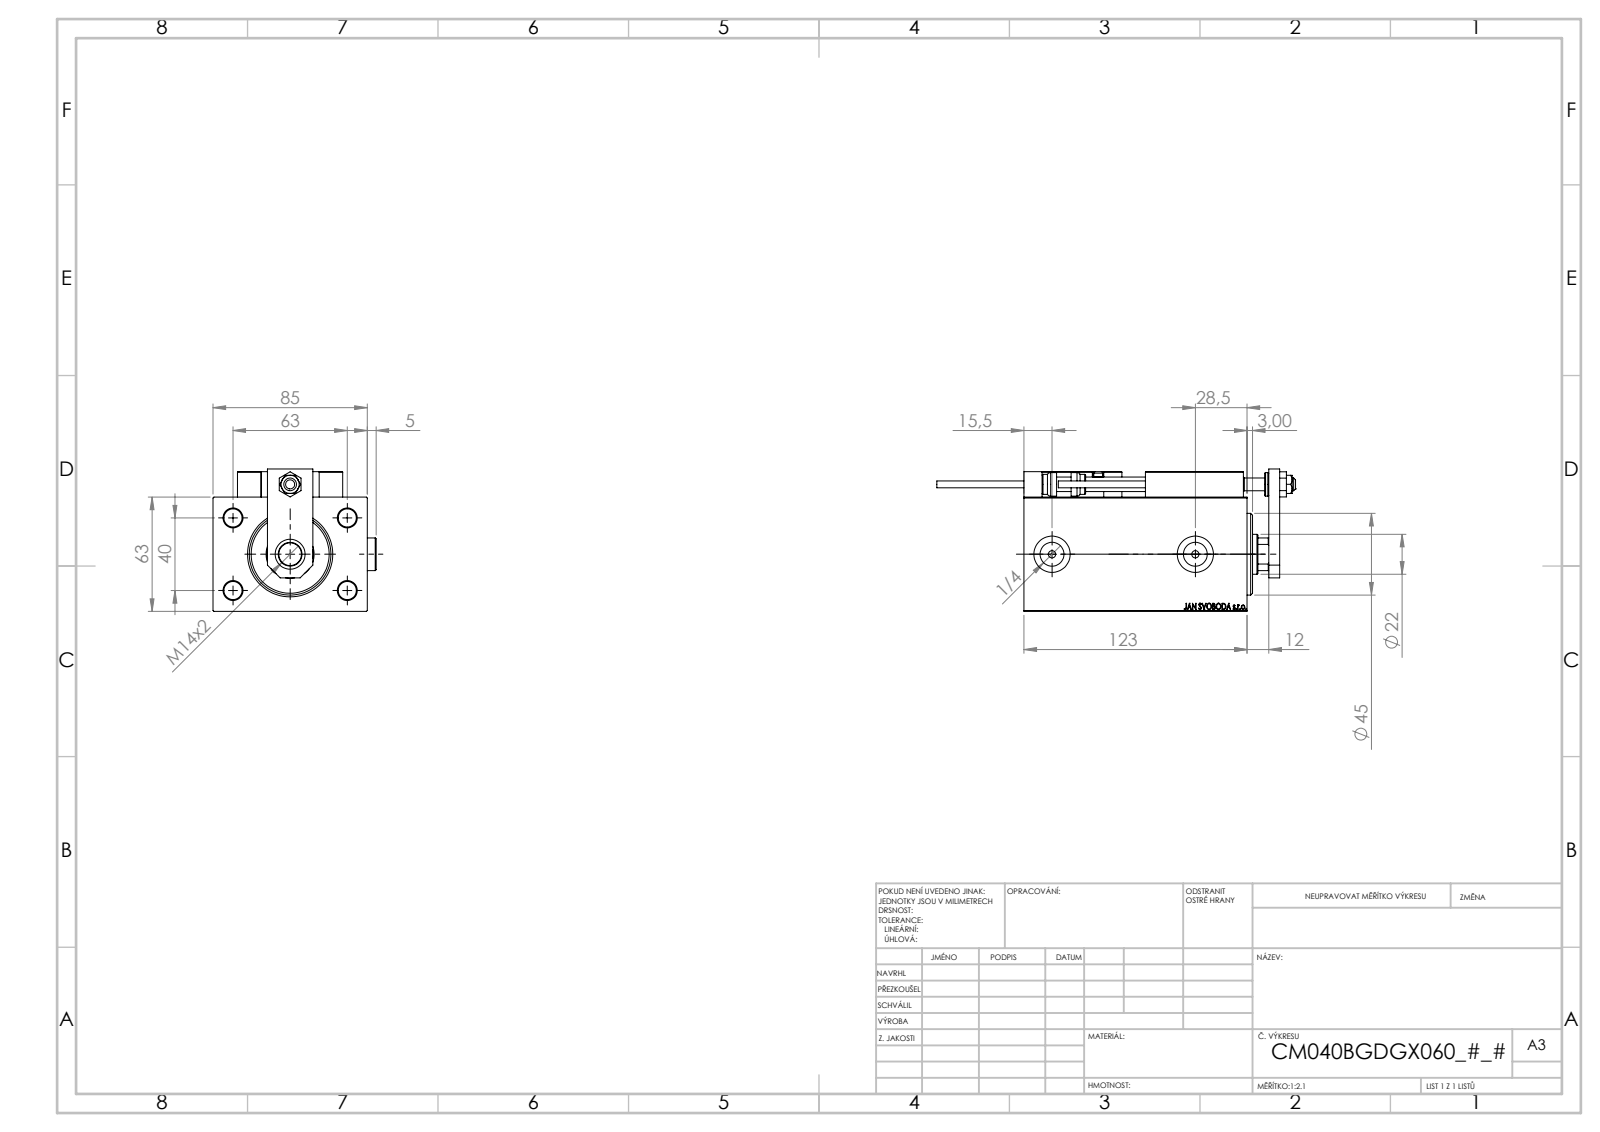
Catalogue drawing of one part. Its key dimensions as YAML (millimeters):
part_name: "Block; SWITCH X; MAGNET; V450CM_B_Body (+7 more)"
step_written_by: "SolidWorks 2019 (CONFIG_CONTROL_DESIGN)"
units: millimeters
bodies: {solids: 26, faces: 1372, planar: 595, cylindrical: 200, other: 577}
overall_size: [197.7, 89.9, 78.5]
volume: 642904
surface_area: 115567
round_holes:
  - {diameter: 4, count: 6}
  - {diameter: 8, count: 5}
  - {diameter: 3.2, count: 4}
  - {diameter: 10, count: 4}
  - {diameter: 5, count: 2}
  - {diameter: 13.16, count: 2}
  - {diameter: 20, count: 2}
  - {diameter: 7, count: 1}
  - {diameter: 12.5, count: 1}
  - {diameter: 16.5, count: 1}
  - {diameter: 22, count: 1}
  - {diameter: 25.5, count: 1}
round_bosses_or_shafts:
  - {diameter: 18, count: 2}
  - {diameter: 5, count: 2}
  - {diameter: 3.8, count: 2}
  - {diameter: 13, count: 1}
  - {diameter: 11, count: 1}
partial_cylinders:
  - {radius: 0.3, count: 30}
  - {radius: 3, count: 2}
  - {radius: 10.5, count: 1}
face_to_face_distances: [63, 85, 12, 123, 111, 14, 77, 18, 30, 13.5]
hole_center_spacings: [37.31, 11.37, 20, 29.59, 29.69, 36.06, 36.53, 40]
